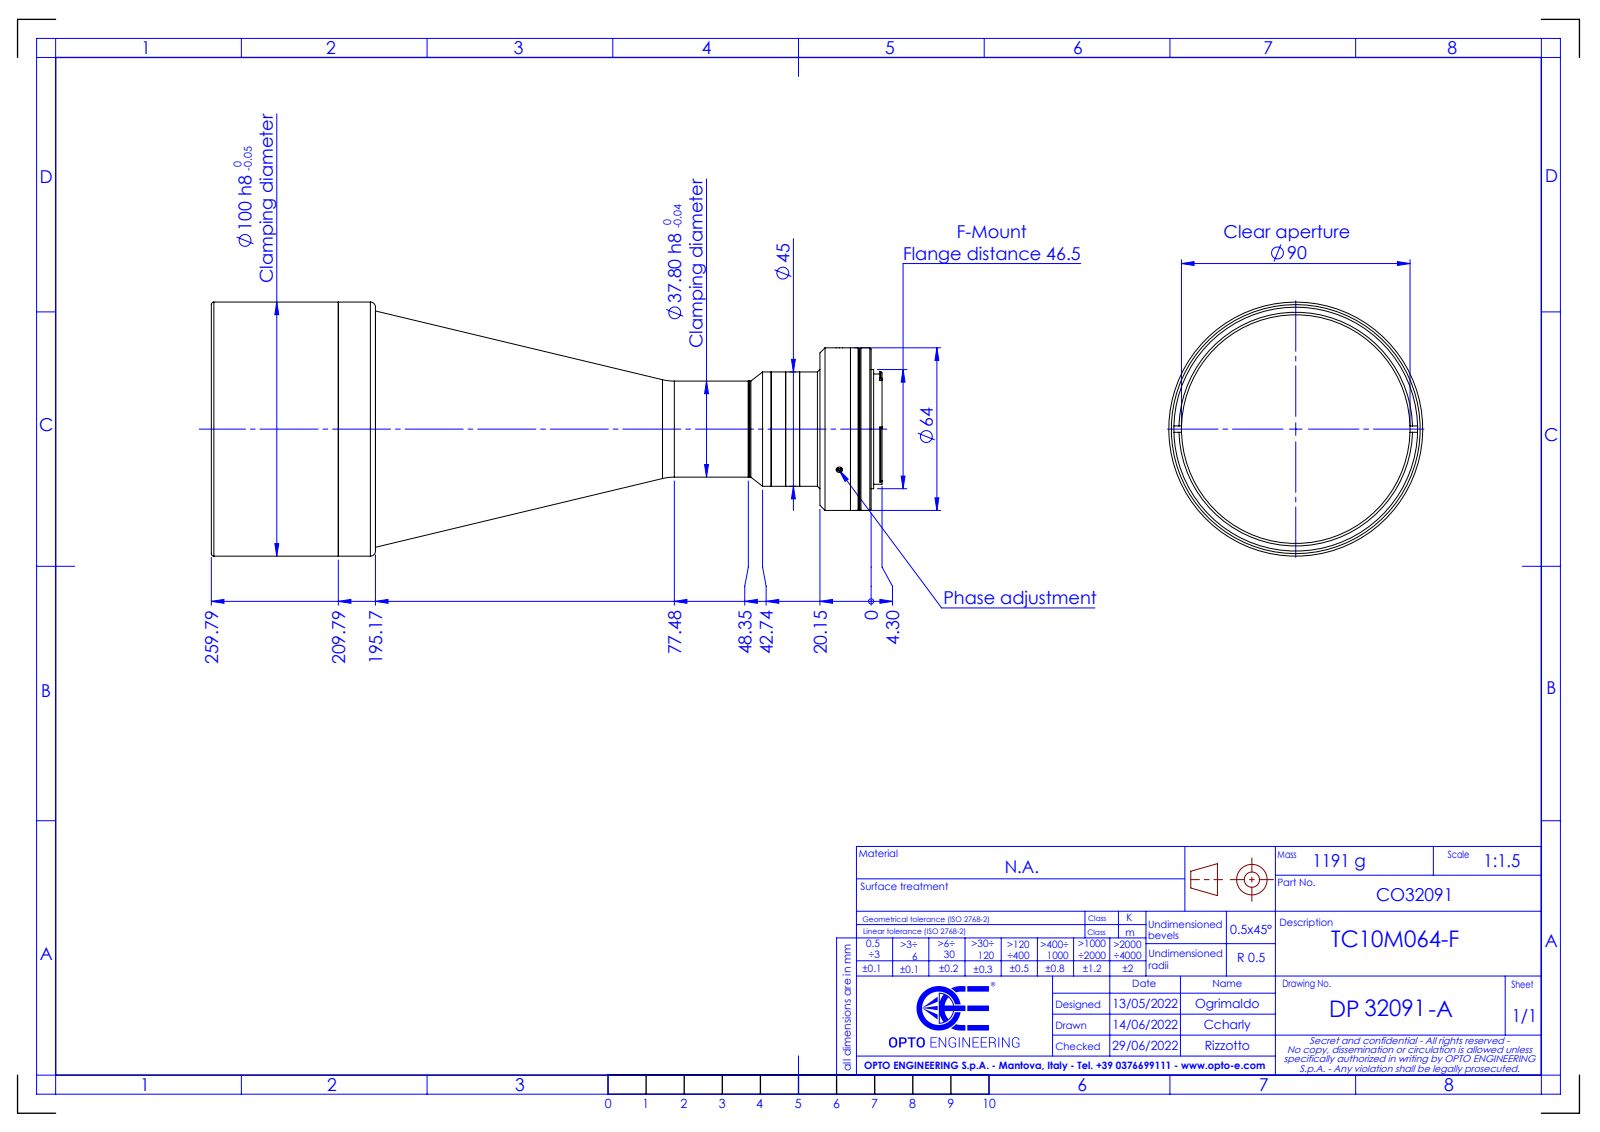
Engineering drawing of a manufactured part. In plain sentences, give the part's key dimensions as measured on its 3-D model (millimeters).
The part is named "DP32091-A_TC10M064-F". Its 3-D file was written by "SolidWorks 2021 (CONFIG_CONTROL_DESIGN)". It is 0 solids with 128 faces: 37 planar, 59 cylindrical and 32 other. Overall it measures 264.09 by 100 by 100 millimeters. Round holes: 3 of diameter 2.5, 1 of diameter 33, 1 of diameter 42, 1 of diameter 90, 1 of diameter 96. Round bosses or shafts: 1 of diameter 100, 1 of diameter 93, 1 of diameter 64, 1 of diameter 63.5, 1 of diameter 46.9, 1 of diameter 45, 1 of diameter 43.4, 1 of diameter 37.8. Partial cylindrical surfaces (rounded edges, fillets, slot ends): 2 of radius 1.15, 1 of radius 0.5, 1 of radius 22.65. The main face-to-face distances are 209.79, 251.14, 201.66, 8.13, 204.66, 3, 5.13, 189.64, 12.02, 15.02.
